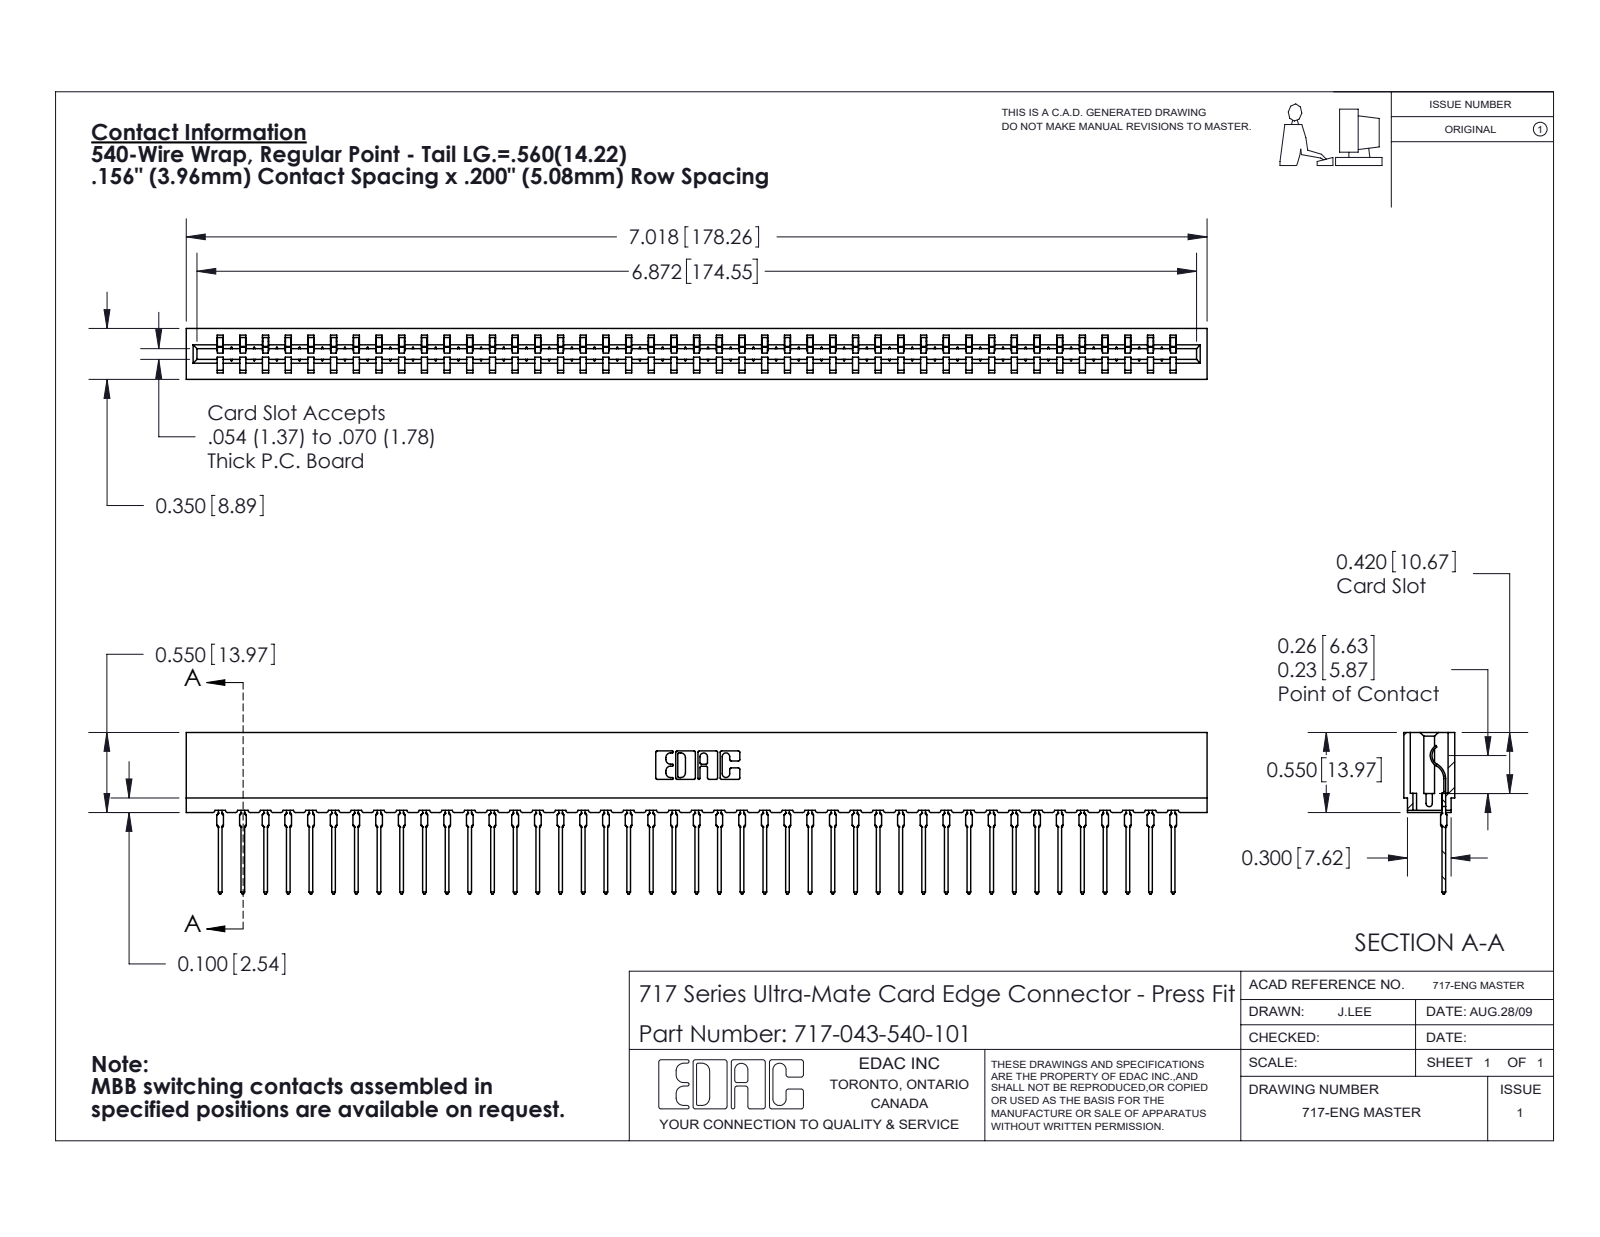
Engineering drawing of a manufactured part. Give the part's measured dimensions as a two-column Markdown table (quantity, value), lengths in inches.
| quantity | value |
| --- | --- |
| part name | 717 Part_Insulator Option - 06; 717-043-540-101; 745-292-001_540 |
| STEP written by | SolidWorks 2020 (CONFIG_CONTROL_DESIGN) |
| units | inches |
| bodies | 44 solids, 4953 faces (2978 planar, 857 cylindrical, 1118 other) |
| overall size | 7.018 × 1.109 × 0.35 |
| volume | 0.924 in³ |
| surface area | 33.77 in² |
| partial cylindrical surfaces (radius × count) | 0.015 × 86, 0.021 × 86, 0.01 × 22, 0.007 × 6, 0.031 × 6, 0.005 × 4, 0.011 × 4, 0.026 × 3 |
| main face-to-face distances | 0.212, 0.138, 0.35, 0.074, 0.063, 0.287, 0.076, 0.149, 0.045, 0.305 |
